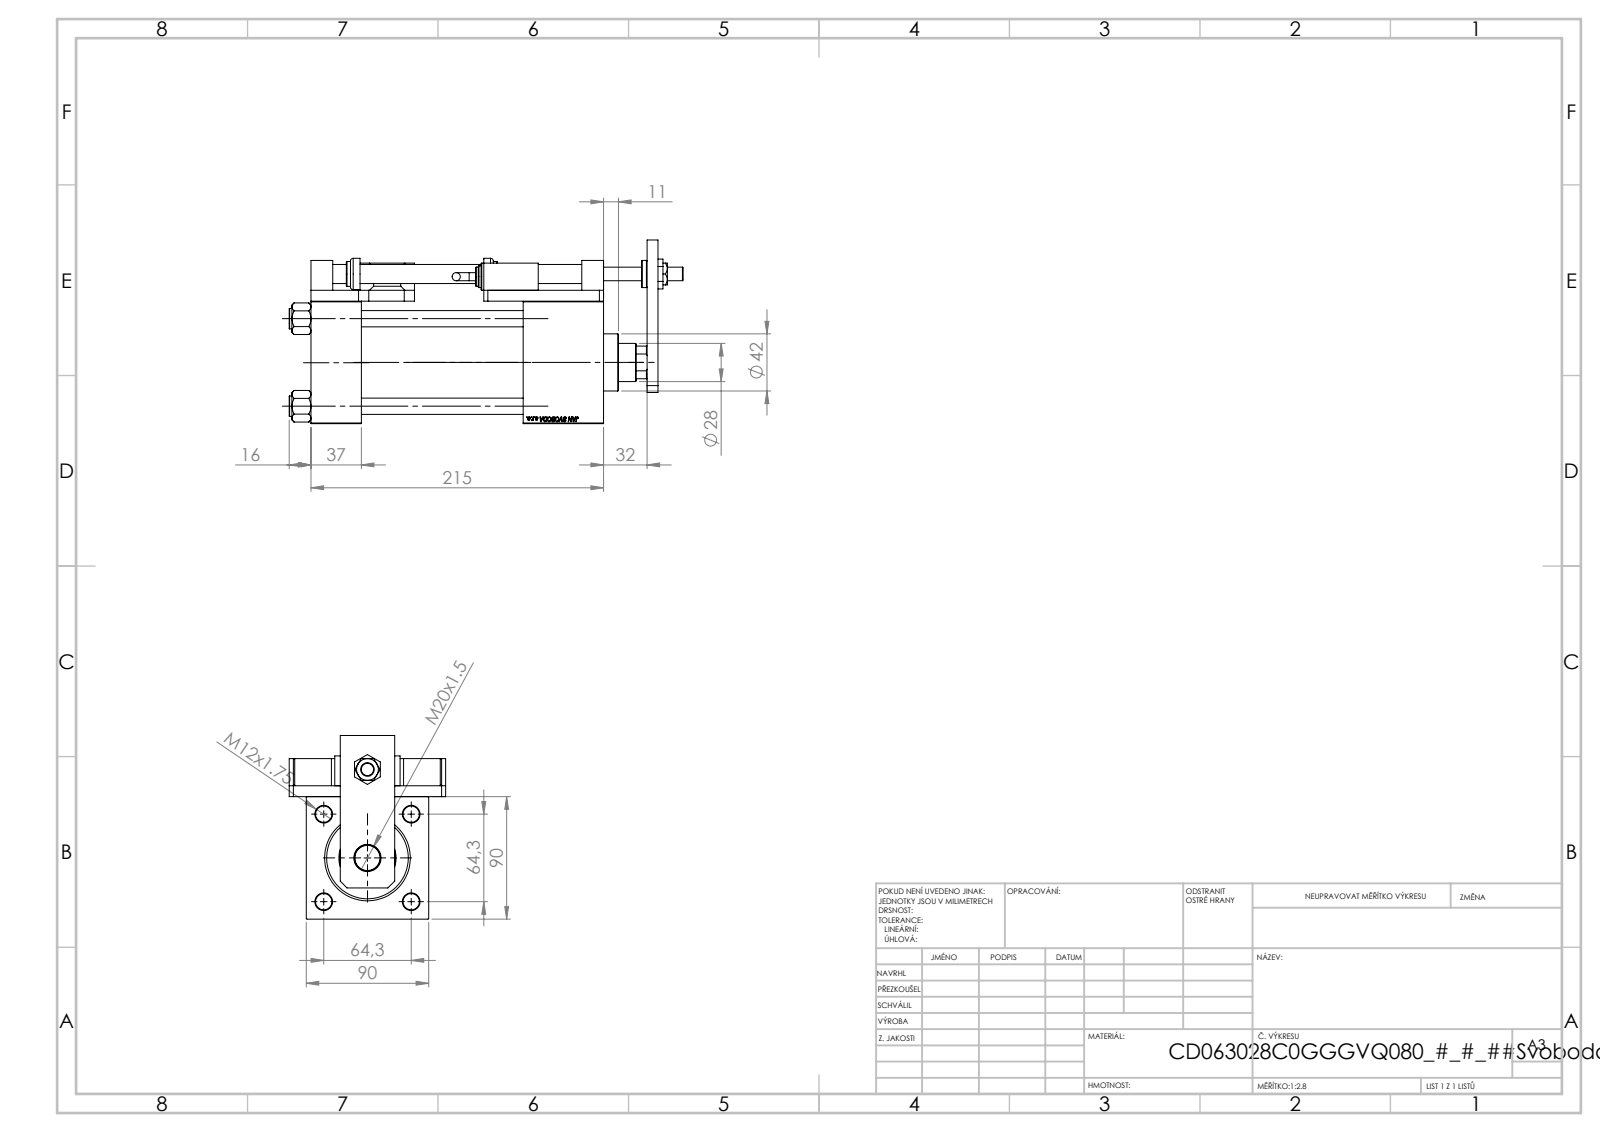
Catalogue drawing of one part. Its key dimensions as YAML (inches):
part_name: "V215CD_VC_C; V215CD_VCP_C; V215CD_Body_C; NUT_M5_V215CD_C (+8 more)"
step_written_by: "SolidWorks 2019 (CONFIG_CONTROL_DESIGN)"
units: inches
bodies: {solids: 24, faces: 1377, planar: 647, cylindrical: 155, other: 575}
overall_size: [11.398, 5.315, 4.528]
volume: 80.73
surface_area: 474.6
round_holes:
  - {diameter: 0.335, count: 4}
  - {diameter: 0.472, count: 4}
  - {diameter: 0.531, count: 4}
  - {diameter: 0.276, count: 2}
  - {diameter: 0.825, count: 2}
  - {diameter: 1.181, count: 2}
  - {diameter: 0.394, count: 1}
  - {diameter: 0.551, count: 1}
  - {diameter: 0.728, count: 1}
  - {diameter: 0.787, count: 1}
  - {diameter: 1.102, count: 1}
  - {diameter: 1.22, count: 1}
round_bosses_or_shafts:
  - {diameter: 0.591, count: 4}
  - {diameter: 0.787, count: 3}
  - {diameter: 0.63, count: 2}
  - {diameter: 0.551, count: 2}
  - {diameter: 0.236, count: 2}
  - {diameter: 2.717, count: 1}
  - {diameter: 1.654, count: 1}
  - {diameter: 0.906, count: 1}
partial_cylinders:
  - {radius: 0.295, count: 4}
  - {radius: 0.531, count: 1}
face_to_face_distances: [0.315, 3.543, 1.457, 3.858, 8.465, 7.008, 1.575, 1.26, 3.583, 2.323]
hole_center_spacings: [1.79, 2.531, 0.754, 1.26, 1.374, 1.809, 3.58, 4.029]
